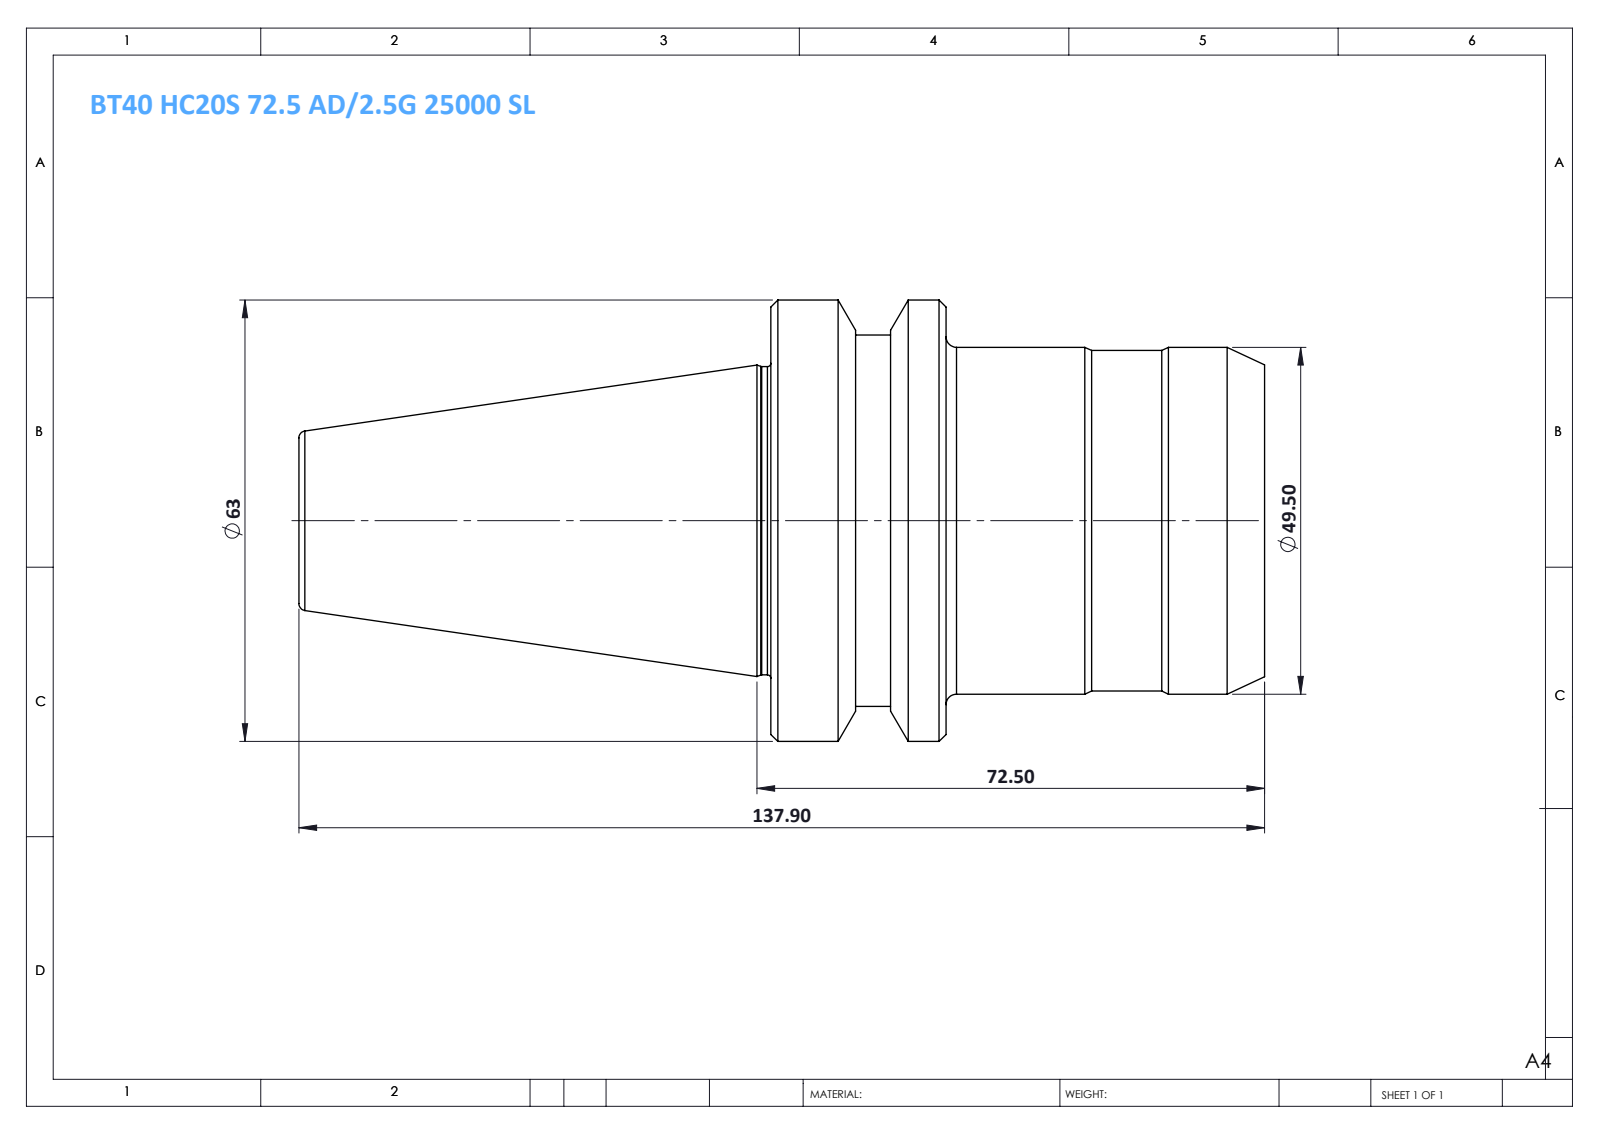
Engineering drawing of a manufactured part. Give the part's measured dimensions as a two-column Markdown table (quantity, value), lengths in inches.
| quantity | value |
| --- | --- |
| part name | BT40 HC20S 72.5 AD 2.5G 25000 SL |
| STEP written by | SolidWorks 2014 (CONFIG_CONTROL_DESIGN) |
| units | inches |
| bodies | 1 solid, 46 faces (6 planar, 14 cylindrical, 26 other) |
| overall size | 5.429 × 2.48 × 2.48 |
| volume | 13.68 in³ |
| surface area | 38.72 in² |
| round bosses / shafts (diameter × count) | 2.48 × 1, 2.087 × 1, 1.949 × 1, 1.913 × 1, 1.732 × 1 |
| main face-to-face distances | 2.776, 1.791, 0.984, 5.429, 3.638, 2.654, 2.102, 0.311, 0.673, 3.327 |
